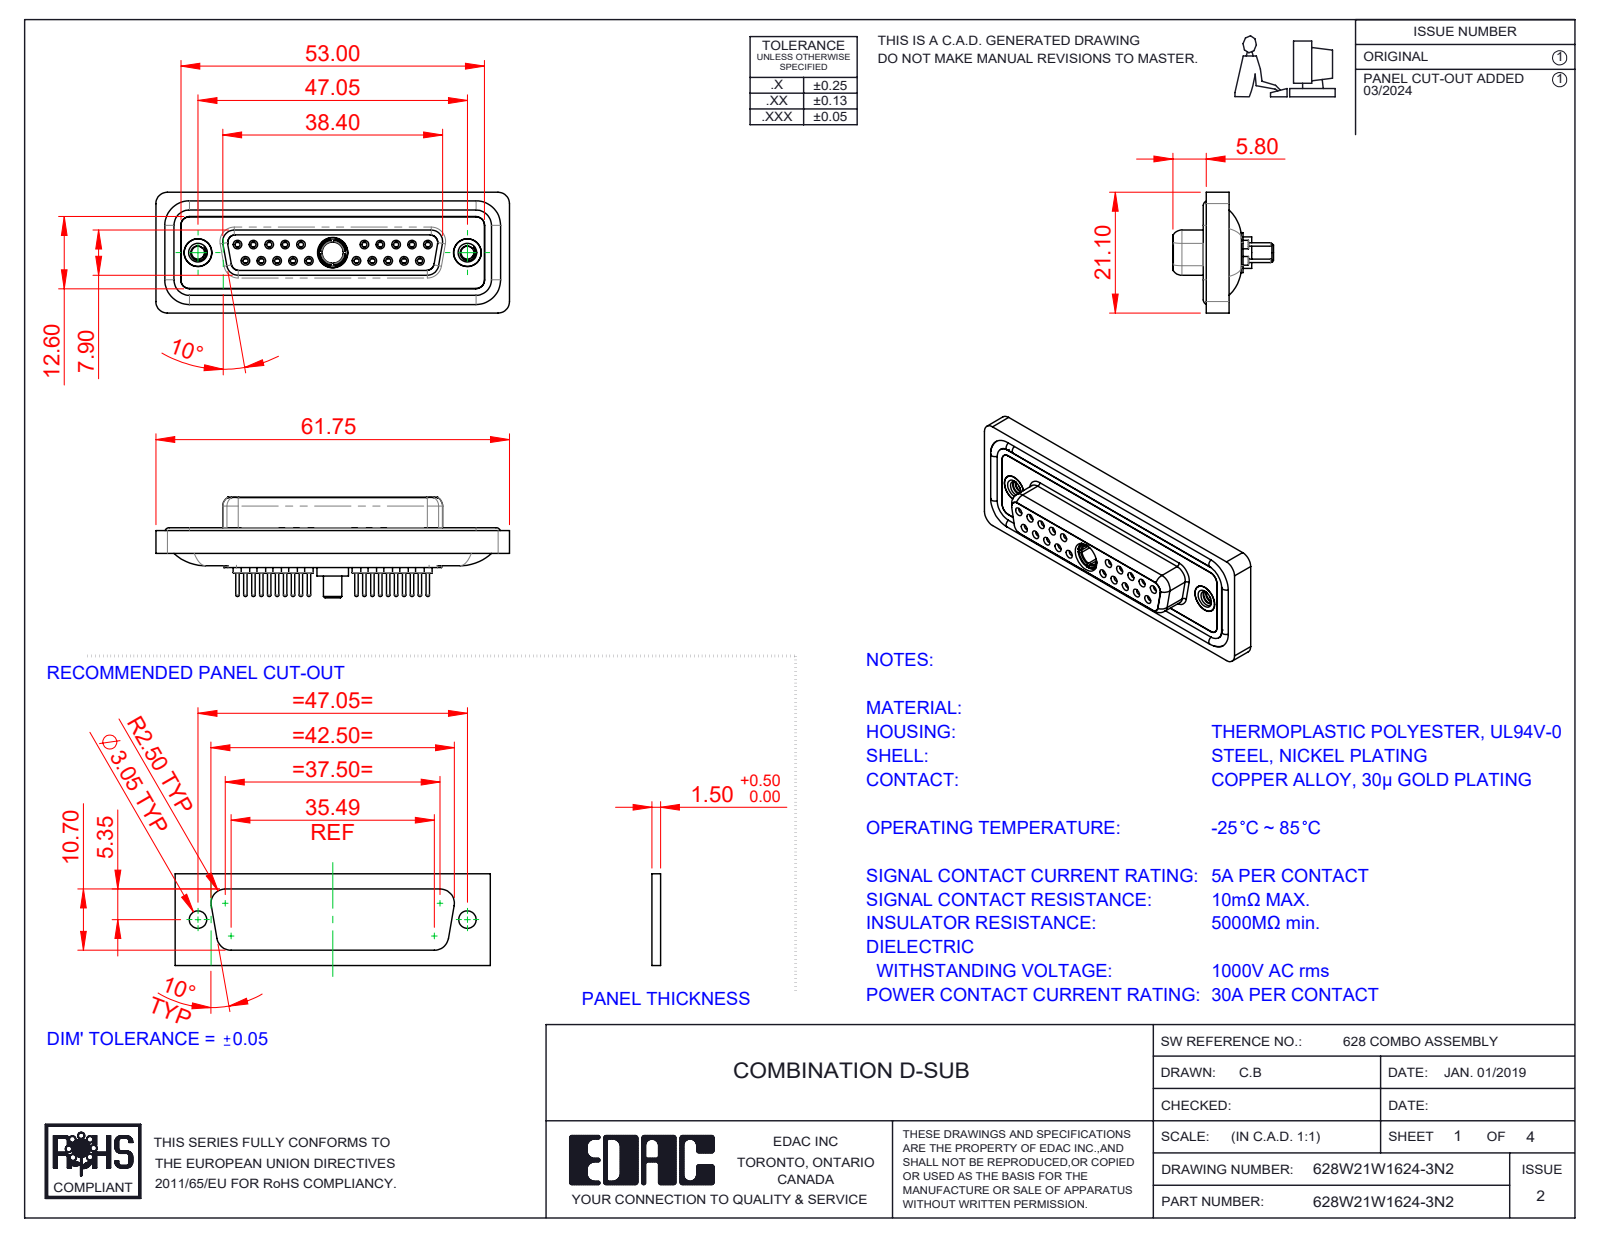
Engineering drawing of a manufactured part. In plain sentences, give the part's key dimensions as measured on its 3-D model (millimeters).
The part is named "Power Socket_30A S; 628W21W1624-3N2; 628Combo Housing_21W1; 628Combo Contact Row 2_24 (+5 more)". Its 3-D file was written by "SolidWorks 2023 (CONFIG_CONTROL_DESIGN)". It is 29 solids with 1560 faces: 434 planar, 591 cylindrical and 535 other. Overall it measures 61.75 by 21.1 by 17.55 millimeters. Its volume is 8 381 cubic millimeters and its surface area 14 006 square millimeters. Round holes: 20 of diameter 0.9, 20 of diameter 1.1, 20 of diameter 1.5, 20 of diameter 2, 10 of diameter 1.6, 10 of diameter 1.7, 3 of diameter 4.85, 2 of diameter 2.26, 2 of diameter 4, 2 of diameter 4.05, 2 of diameter 5, 1 of diameter 3.7. Round bosses or shafts: 20 of diameter 2.2, 20 of diameter 0.6, 14 of diameter 1.6, 2 of diameter 4.95, 2 of diameter 4.8, 1 of diameter 5.5, 1 of diameter 5.2, 1 of diameter 4.96. Partial cylindrical surfaces (rounded edges, fillets, slot ends): 22 of radius 1.5, 18 of radius 2, 8 of radius 1.35, 8 of radius 1.6, 4 of radius 0.25, 4 of radius 0.5, 4 of radius 0.6, 4 of radius 0.65. The main face-to-face distances are 0.4, 1.8, 7.45, 6.6, 5.65, 0.5, 1.6, 7.05, 2.9, 1.1. The hole center spacings are 3.16, 2.77, 5.54, 5.03, 8.31, 7.48, 16.62, 19.39.
